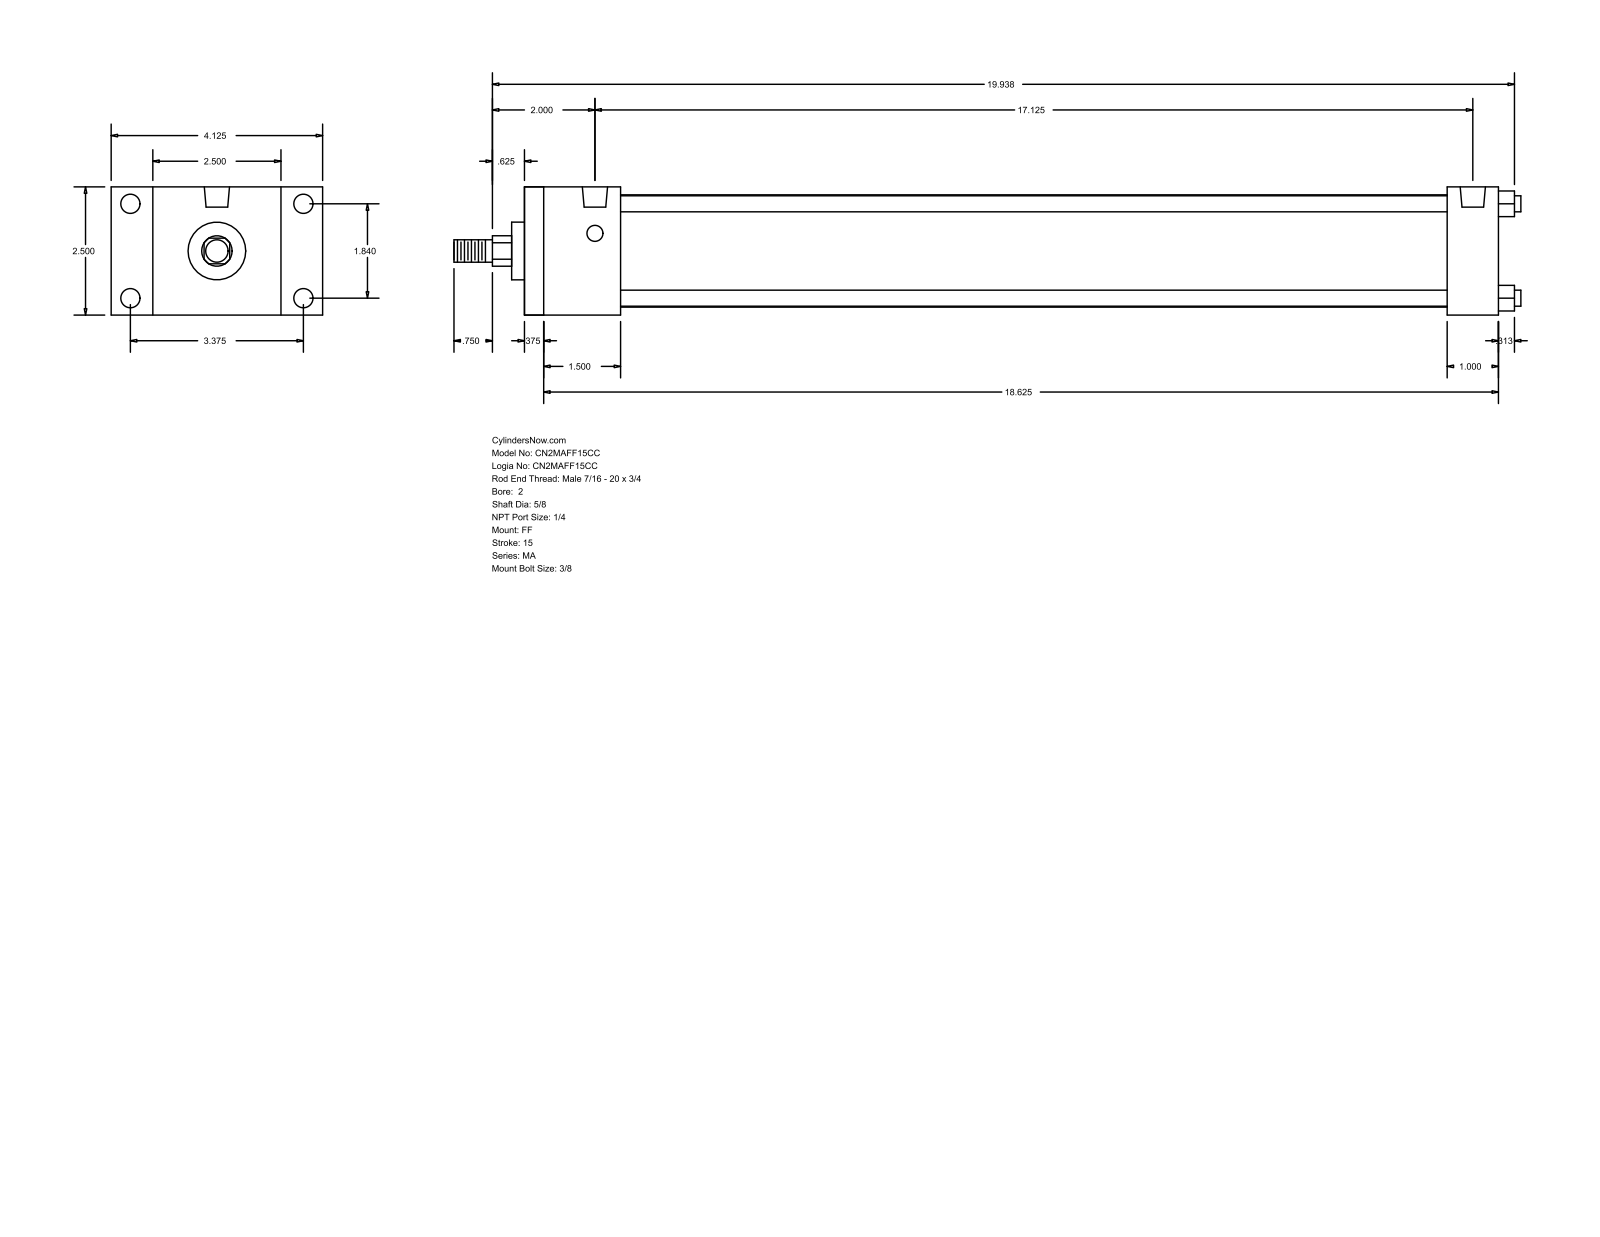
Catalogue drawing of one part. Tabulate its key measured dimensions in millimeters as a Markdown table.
| quantity | value |
| --- | --- |
| part name | MA_FF__0200_0.625 |
| STEP written by | GSSL Pune (CONFIG_CONTROL_DESIGN) |
| units | millimeters |
| bodies | 0 solids, 92 faces (64 planar, 28 cylindrical, 0 other) |
| overall size | 528.64 × 104.78 × 63.5 |
| round holes (diameter × count) | 7.94 × 4, 9.53 × 4, 12.49 × 2 |
| round bosses / shafts (diameter × count) | 7.94 × 4, 55.63 × 1, 28.57 × 1, 15.88 × 1, 11.11 × 1 |
| partial cylindrical surfaces (radius × count) | 7.54 × 1 |
| main face-to-face distances | 63.5, 482.6, 9.52, 473.08, 38.1, 47.62, 457.19, 447.67, 409.57, 434.98 |
| hole center spacings | 46.74, 85.72, 97.63, 434.97 |
